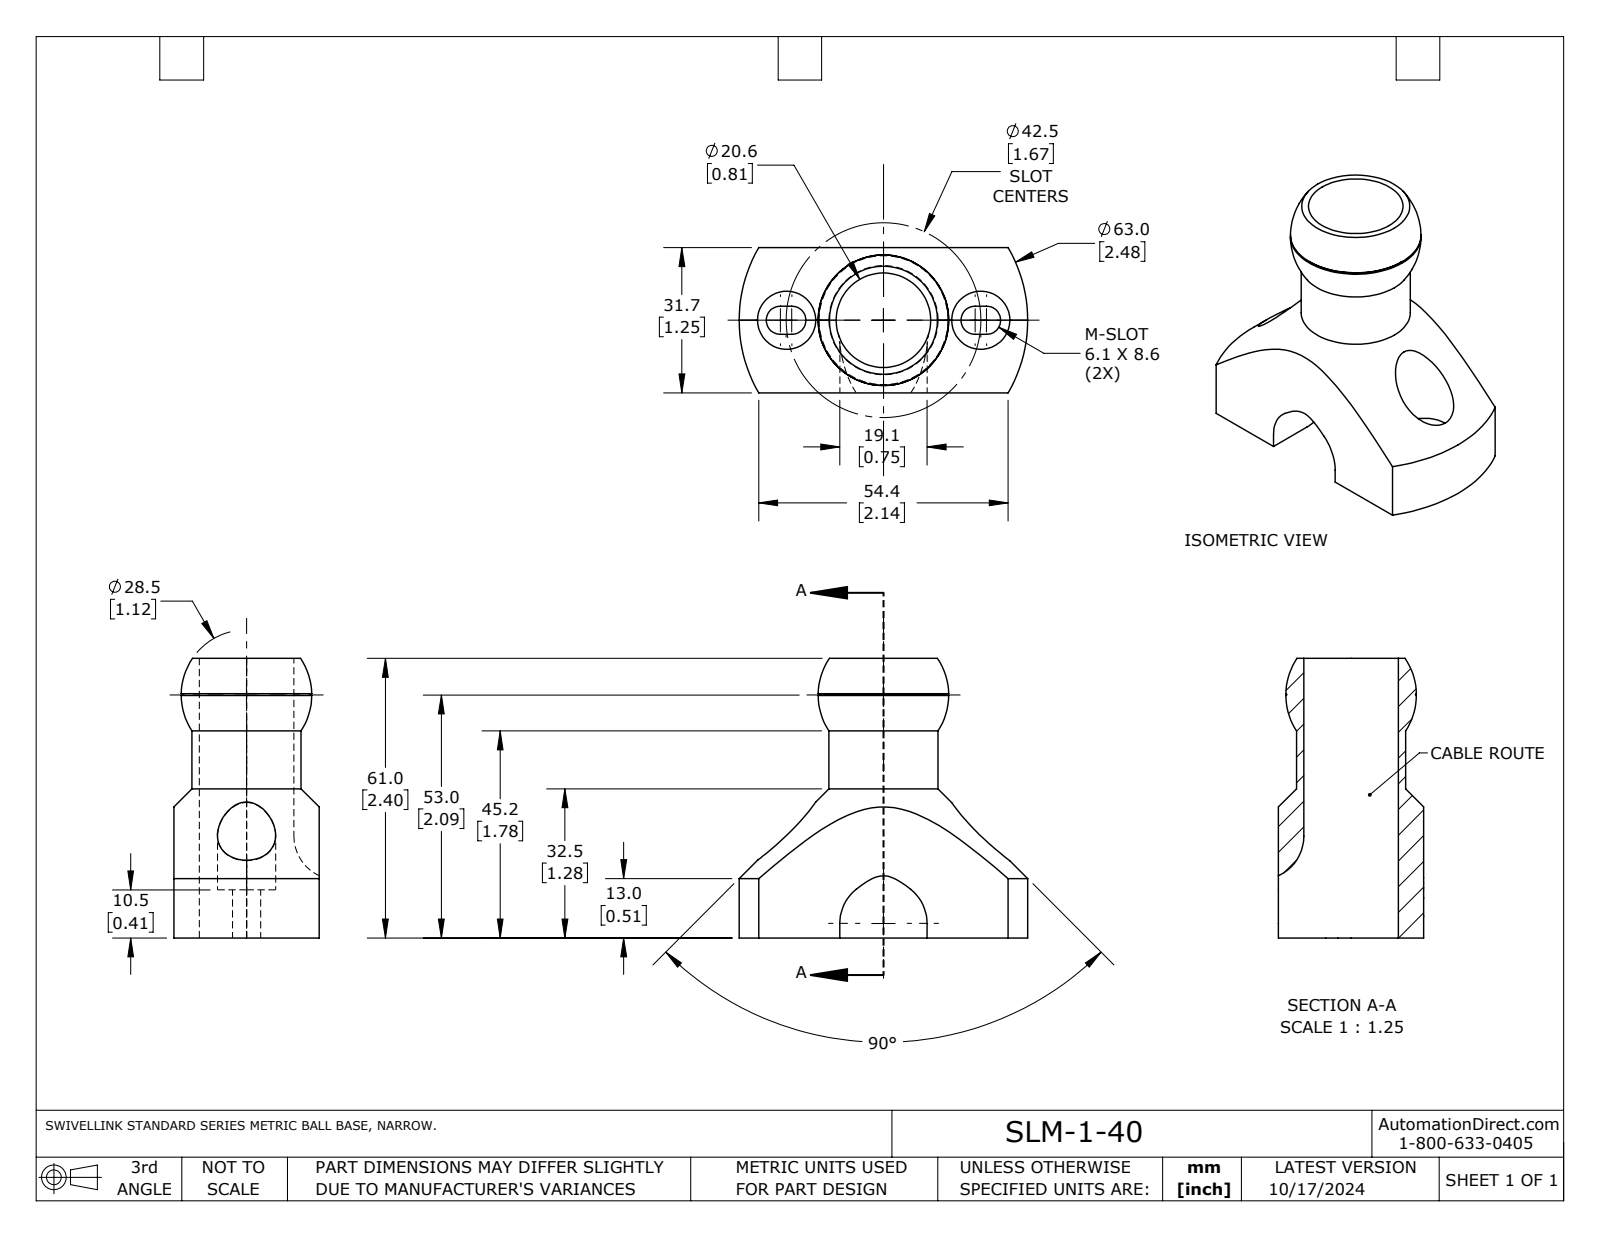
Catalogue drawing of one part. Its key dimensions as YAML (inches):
part_name: "SLM-1-40"
step_written_by: "SolidWorks 2021 (AUTOMOTIVE_DESIGN)"
units: inches
bodies: {solids: 1, faces: 117, planar: 85, cylindrical: 21, other: 11}
overall_size: [2.48, 2.402, 1.248]
volume: 2.263
surface_area: 22.2
round_holes:
  - {diameter: 0.5, count: 2}
  - {diameter: 0.813, count: 1}
round_bosses_or_shafts:
  - {diameter: 0.937, count: 1}
partial_cylinders:
  - {radius: 0.121, count: 4}
  - {radius: 0.375, count: 3}
  - {radius: 1.24, count: 1}
face_to_face_distances: [1.248, 0.413, 0.503, 0.745, 2.402, 1.989, 0.242, 0.75]
hole_center_spacings: [0.832, 0.837, 1.669]
